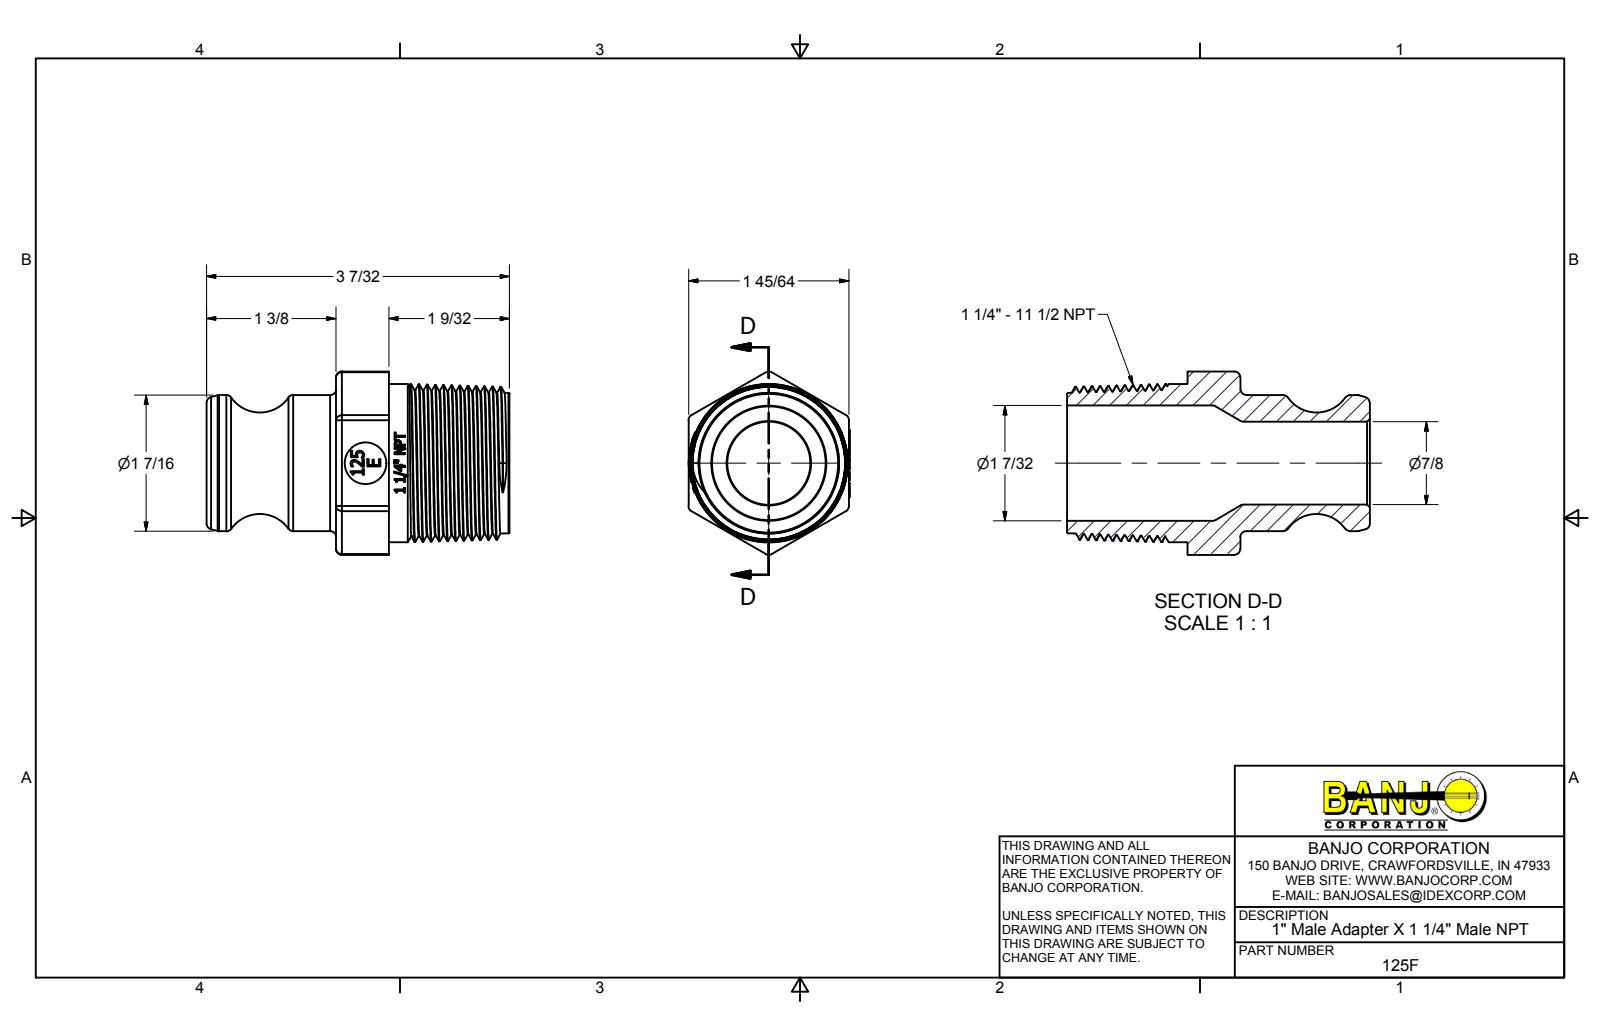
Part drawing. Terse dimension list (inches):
name: 125F
written by: Autodesk Inventor 2014 (AUTOMOTIVE_DESIGN)
unit: in
bodies: 1 solid, 290 faces (157 planar, 30 cylindrical, 103 other)
size: 3.217 × 1.947 × 1.713
volume: 2.953 in³; area: 33.34 in²
holes: 1× ⌀0.44, 1× ⌀0.88, 1× ⌀1.224
bosses: 1× ⌀1.68, 1× ⌀1.446
rounds: 12× R0.063, 1× R0.436, 1× R0.85
face distances: 1.703, 3.217, 1.937, 1.28, 1.375, 0.563, 1.843, 1.693, 1.703, 1.713
